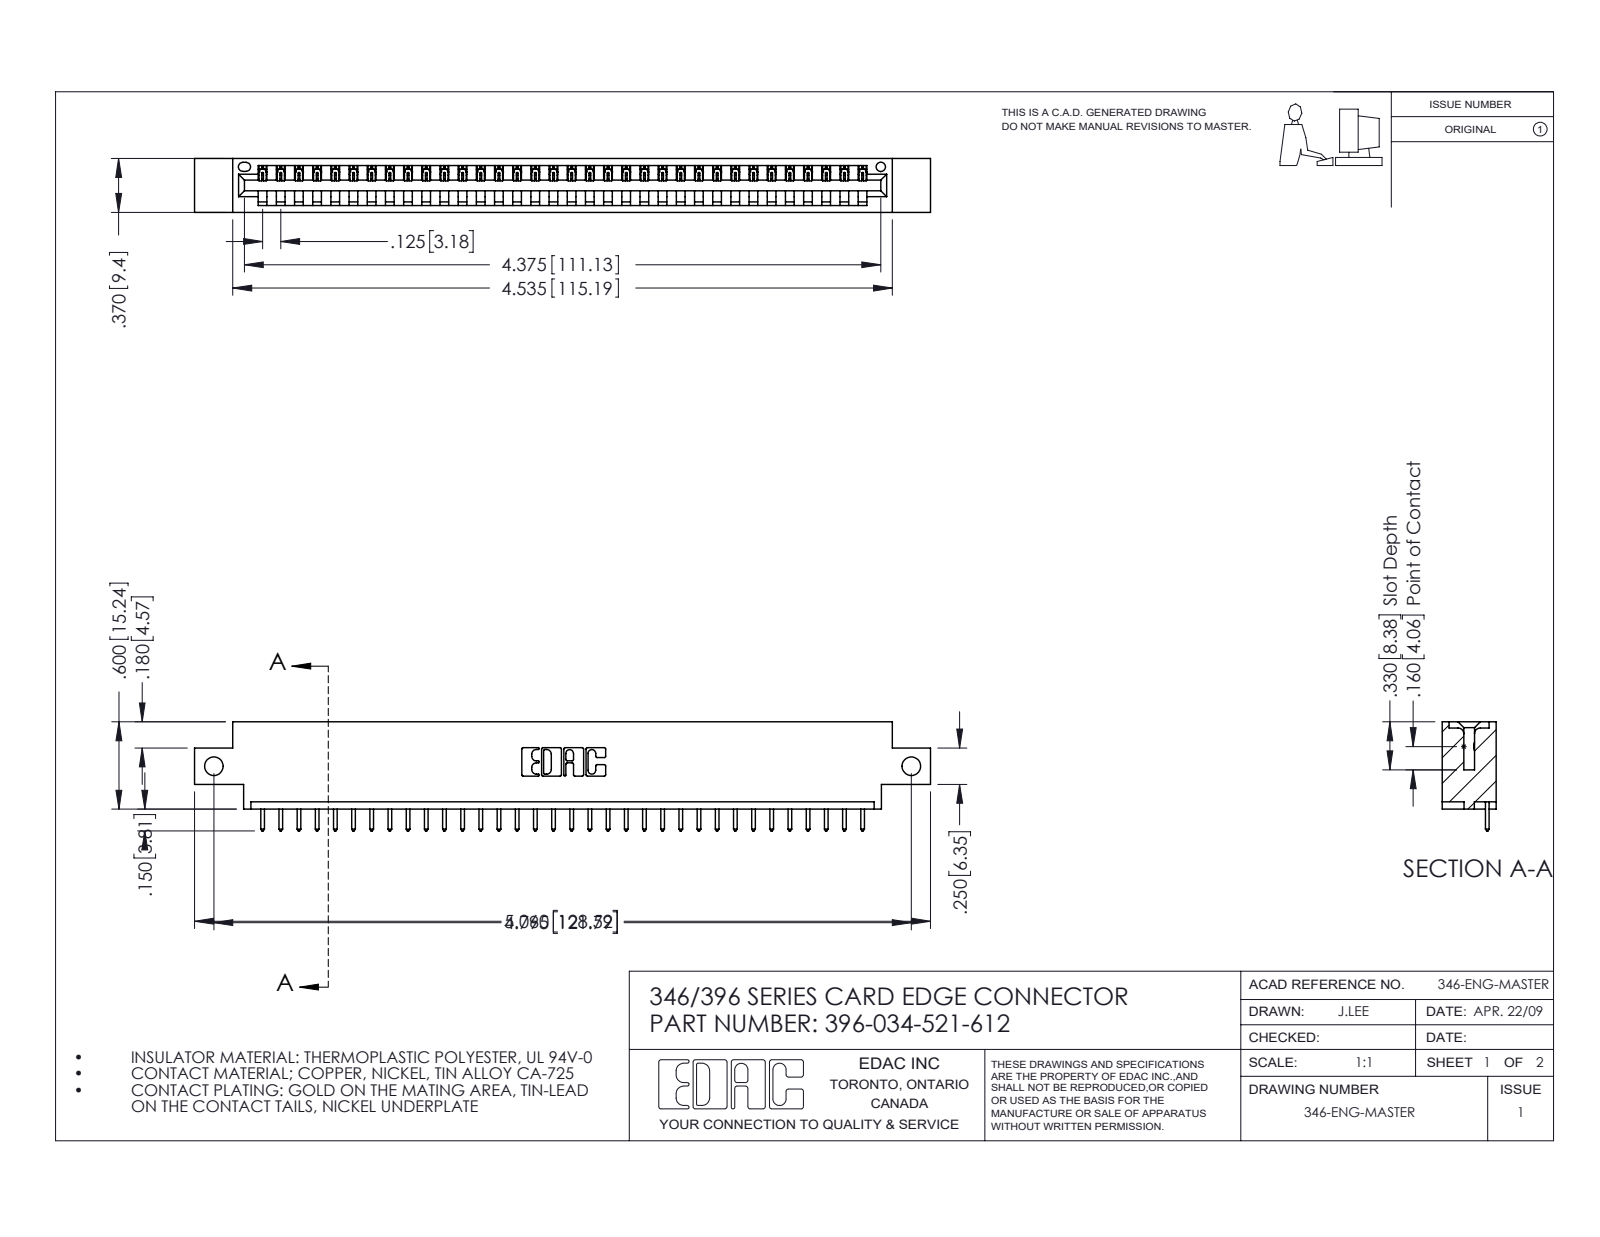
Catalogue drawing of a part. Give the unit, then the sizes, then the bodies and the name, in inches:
Units: inches
Overall size (bounding box): 5.06 × 0.75 × 0.37
Round holes (diameter × count): ⌀0.128 ×2, ⌀0.064 ×1
Partial cylindrical surfaces — rounded edges, fillets, slot ends (radius × count): R0.006 ×68, R0.01 ×68, R0.01 ×22, R0.007 ×6, R0.031 ×6, R0.026 ×3, R0.031 ×2, R0.04 ×2
Main face-to-face distances: 0.048, 0.322, 0.37, 0.25, 0.072, 0.298, 0.025, 0.148, 0.222, 0.1
Hole centre spacings: 4.795
Volume: 0.727 in³ · Surface area: 22.36 in²
Bodies: 35 solids, 2098 faces (1440 planar, 658 cylindrical, 0 other)
Part name (STEP PRODUCT): 396-034-521-612; 345-292-001_345-293-121; 346 Part_0.170 Offset - Side Mount
STEP written by: SolidWorks 2016 (CONFIG_CONTROL_DESIGN)
